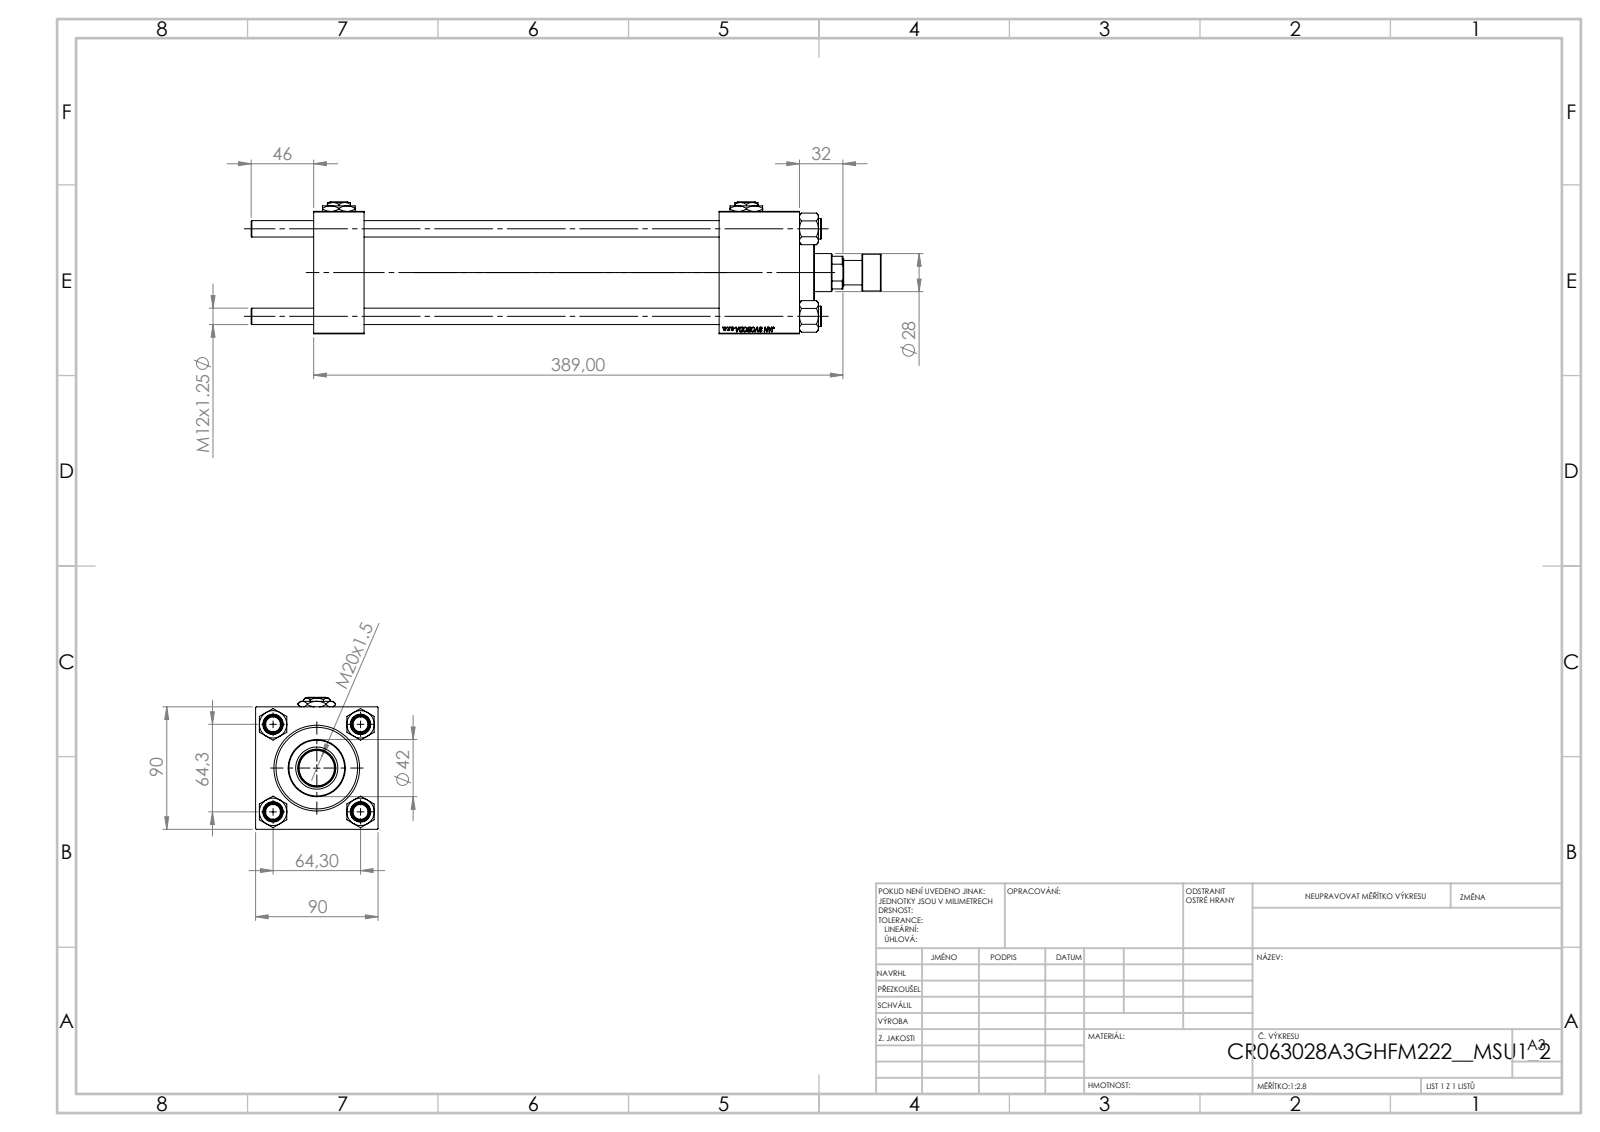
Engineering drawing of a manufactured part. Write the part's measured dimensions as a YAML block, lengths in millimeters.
part_name: "V215_VC_A; CR025_012_A_0_G_A_G_M_020_+#_##_TYCINKA; NUT_M5; V215CR_VCP (+3 more)"
step_written_by: "SolidWorks 2019 (CONFIG_CONTROL_DESIGN)"
units: millimeters
bodies: {solids: 14, faces: 1247, planar: 571, cylindrical: 92, other: 584}
overall_size: [463, 97, 90]
volume: 1328000
surface_area: 335305
round_holes:
  - {diameter: 12, count: 4}
  - {diameter: 7, count: 2}
  - {diameter: 20.96, count: 2}
  - {diameter: 30, count: 2}
  - {diameter: 18.5, count: 1}
  - {diameter: 28, count: 1}
  - {diameter: 31, count: 1}
  - {diameter: 50, count: 1}
  - {diameter: 60, count: 1}
  - {diameter: 63, count: 1}
round_bosses_or_shafts:
  - {diameter: 15, count: 4}
  - {diameter: 69, count: 1}
  - {diameter: 42, count: 1}
  - {diameter: 27, count: 1}
  - {diameter: 18, count: 1}
face_to_face_distances: [90, 37, 357, 320, 59, 298, 261, 328.3, 291.3, 30.3]
hole_center_spacings: [45.47, 64.3, 90.93, 299.5]
